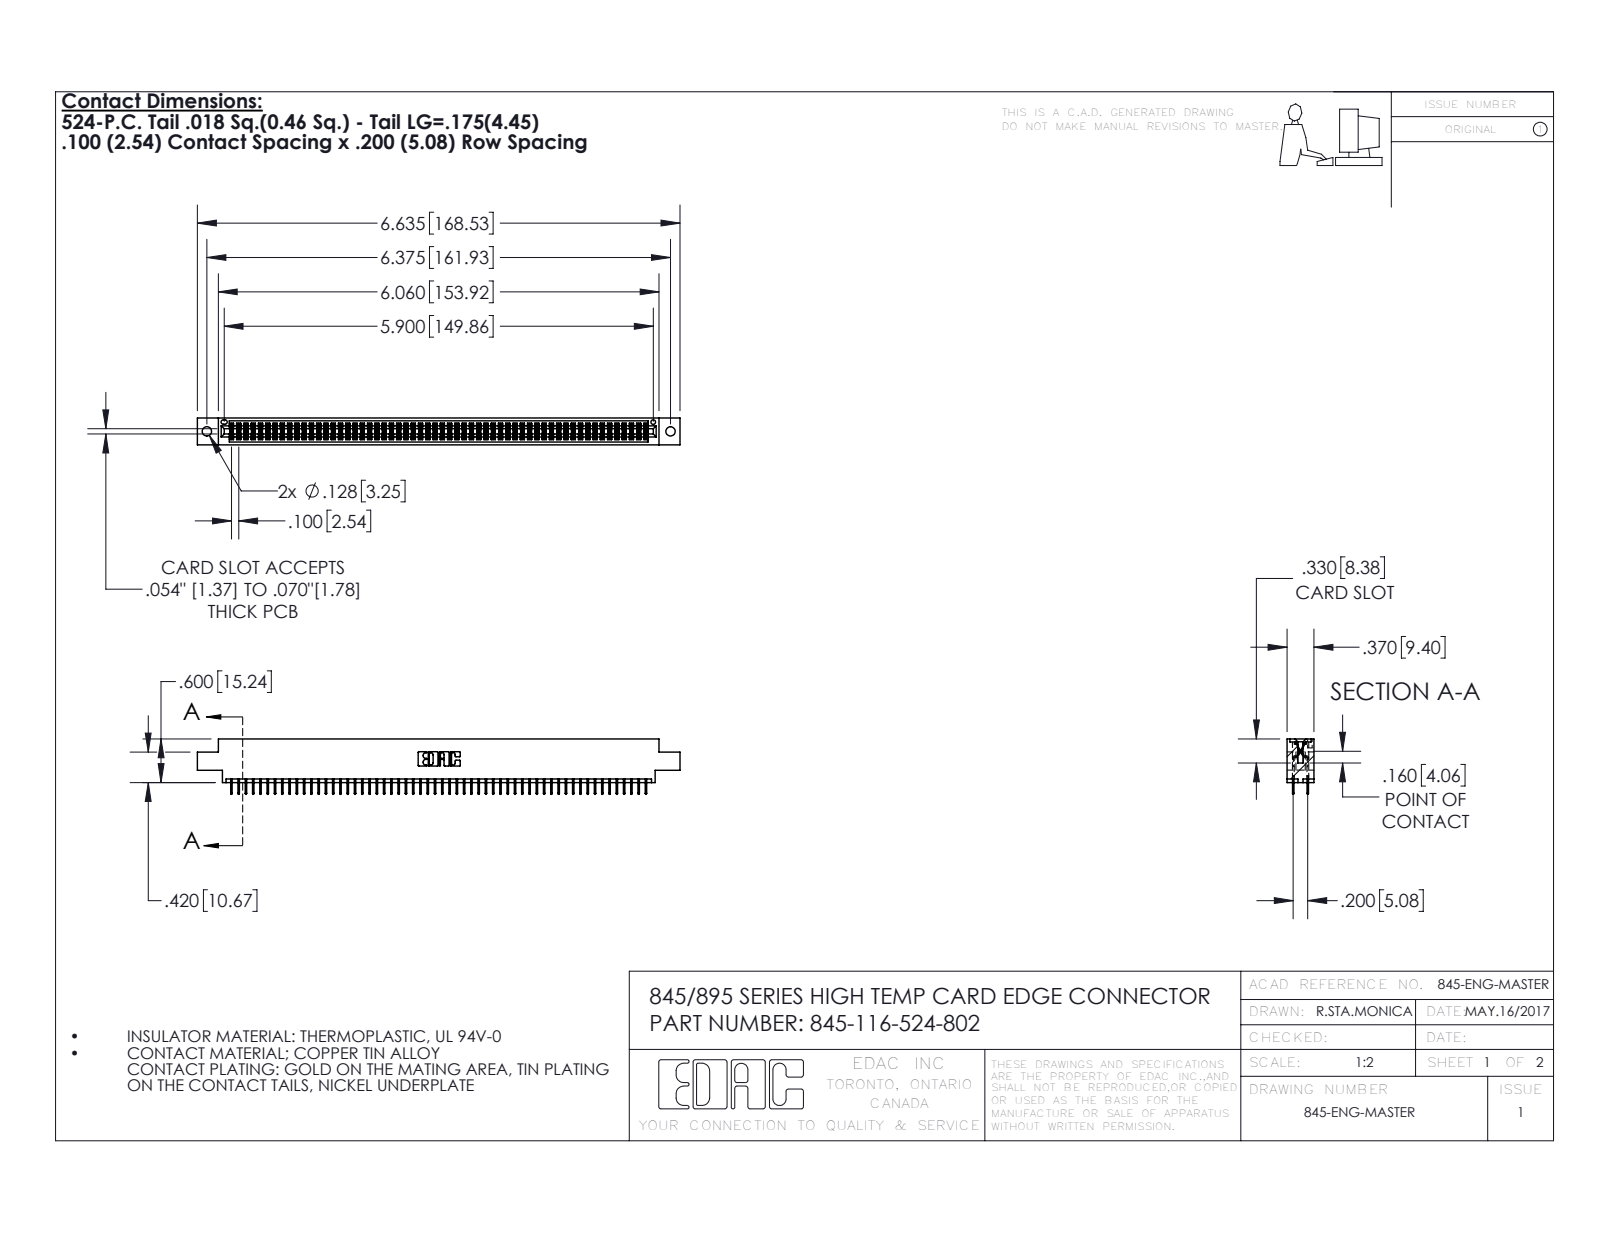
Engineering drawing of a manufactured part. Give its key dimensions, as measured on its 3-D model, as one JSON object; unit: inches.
{"part_name": "345-292-001_345-293-124; 345-116-524-802; 345 Part_0.170 Offset - 0.128 Dia", "step_written_by": "SolidWorks 2016 (CONFIG_CONTROL_DESIGN)", "units": "inches", "bodies": {"solids": 117, "faces": 6394, "planar": 4608, "cylindrical": 1786, "other": 0}, "overall_size": [6.635, 0.762, 0.37], "volume_in3": 0.988, "surface_area_in2": 36.66, "round_holes": [[0.128, 2], [0.064, 1]], "partial_cylinders_radius": [[0.006, 174], [0.01, 22], [0.007, 6], [0.031, 6], [0.026, 3], [0.014, 2], [0.019, 2], [0.022, 2]], "face_to_face_distances": [0.072, 0.298, 0.37, 0.2, 0.098, 0.272, 0.025, 0.225, 0.072, 0.175], "hole_center_spacings": [0.27, 6.139, 6.375]}
